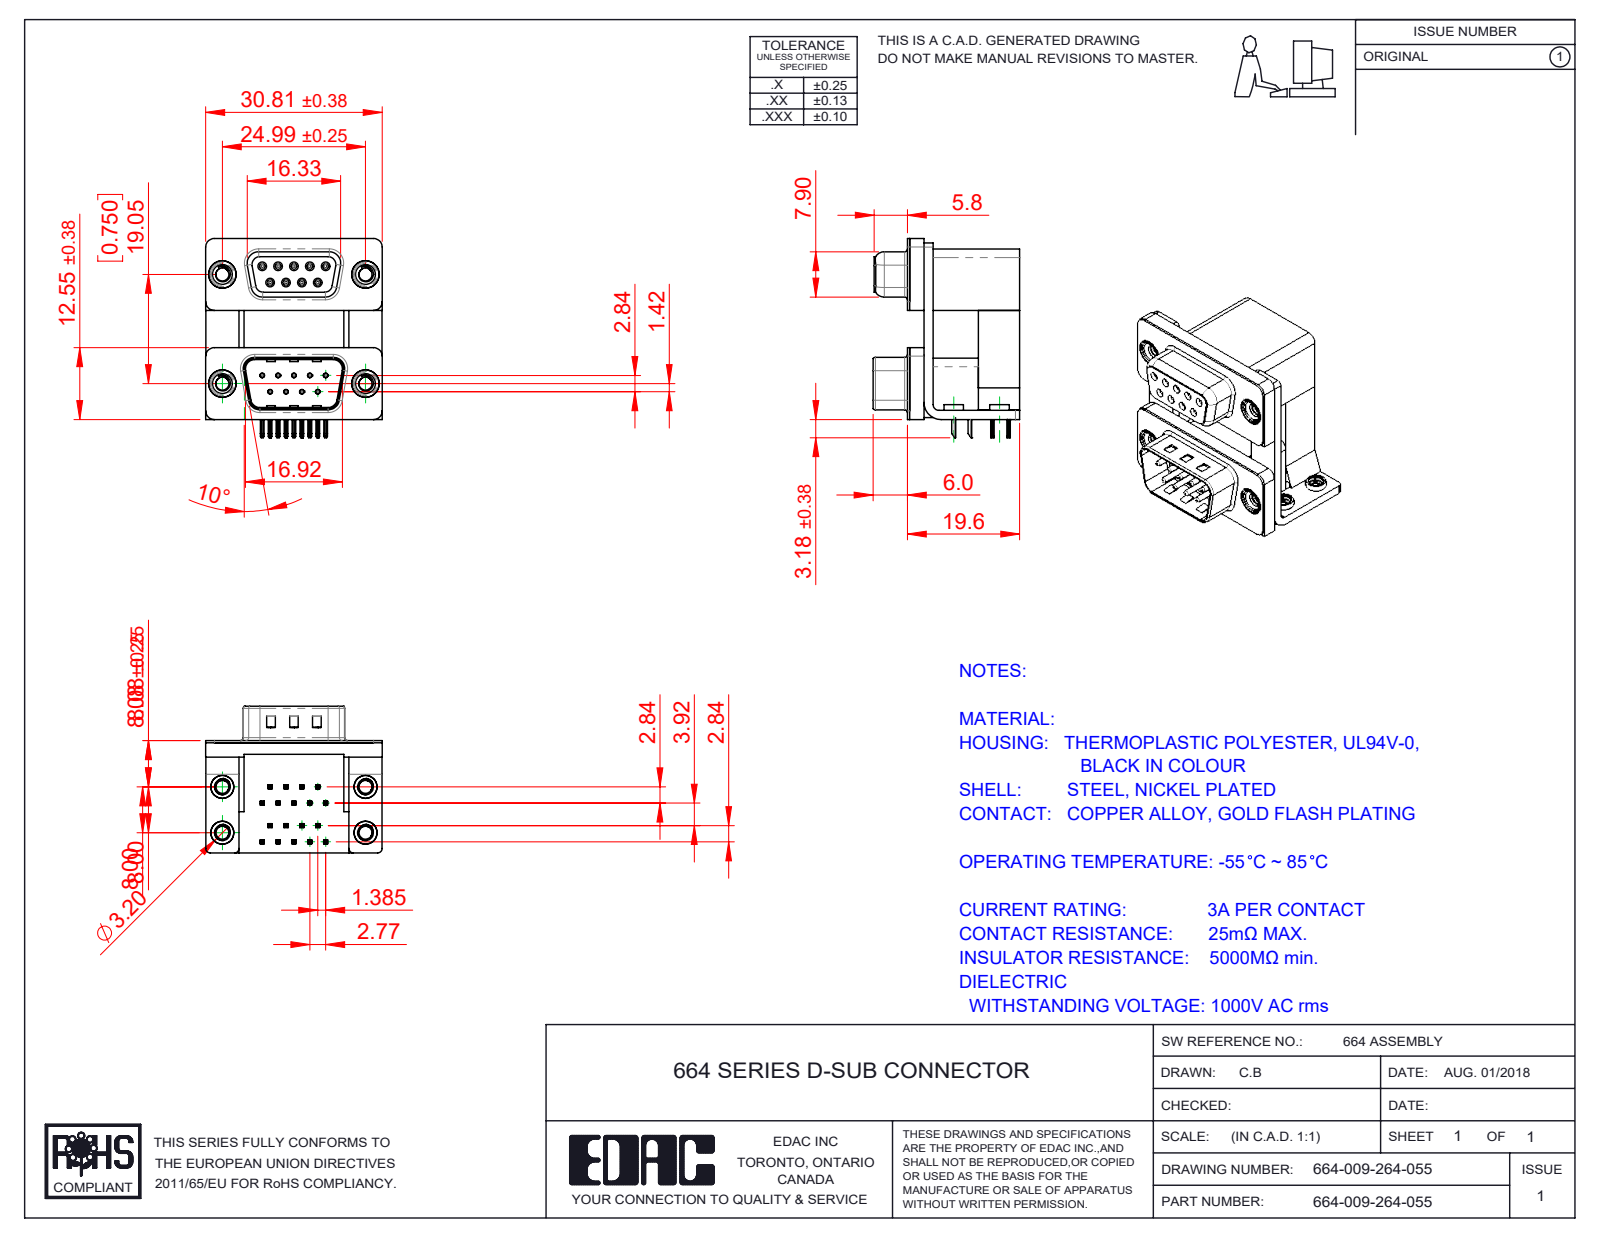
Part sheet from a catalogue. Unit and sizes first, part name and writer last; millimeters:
Units: millimetres
Overall size (bounding box): 34.78 × 30.81 × 25.6
Round holes (diameter × count): ⌀0.8 ×18, ⌀0.35 ×9, ⌀0.9 ×9, ⌀2.26 ×8, ⌀2.75 ×4, ⌀3.2 ×4, ⌀3.5 ×4, ⌀4 ×4, ⌀4.8 ×4, ⌀5 ×4
Round bosses / shafts (diameter × count): ⌀1.2 ×9, ⌀0.75 ×9, ⌀4.9 ×4, ⌀4.75 ×4, ⌀4 ×4, ⌀3.9 ×4, ⌀3.4 ×4
Partial cylindrical surfaces — rounded edges, fillets, slot ends (radius × count): R0.1 ×72, R0.15 ×36, R0.25 ×36, R0.12 ×18, R0.35 ×18, R1.5 ×13, R0.5 ×12, R0.34 ×9
Main face-to-face distances: 0.4, 2.5, 16.7, 19.2, 7.2, 9.5, 12, 1.6, 10.69, 19.6
Hole centre spacings: 3.16, 2.77, 19.25, 19.05, 5.54, 19.84, 16.27, 21.93
Volume: 10 810 mm³ · Surface area: 12 804 mm²
Bodies: 33 solids, 2669 faces (1275 planar, 771 cylindrical, 623 other)
Part name (STEP PRODUCT): 664 Shell Plug_09 Contacts; 664 Contact Bottom Lower; 664 Threaded Rivet_4-40; 664 Contact Bottom Upper_M (+8 more)
STEP written by: SolidWorks 2020 (CONFIG_CONTROL_DESIGN)
